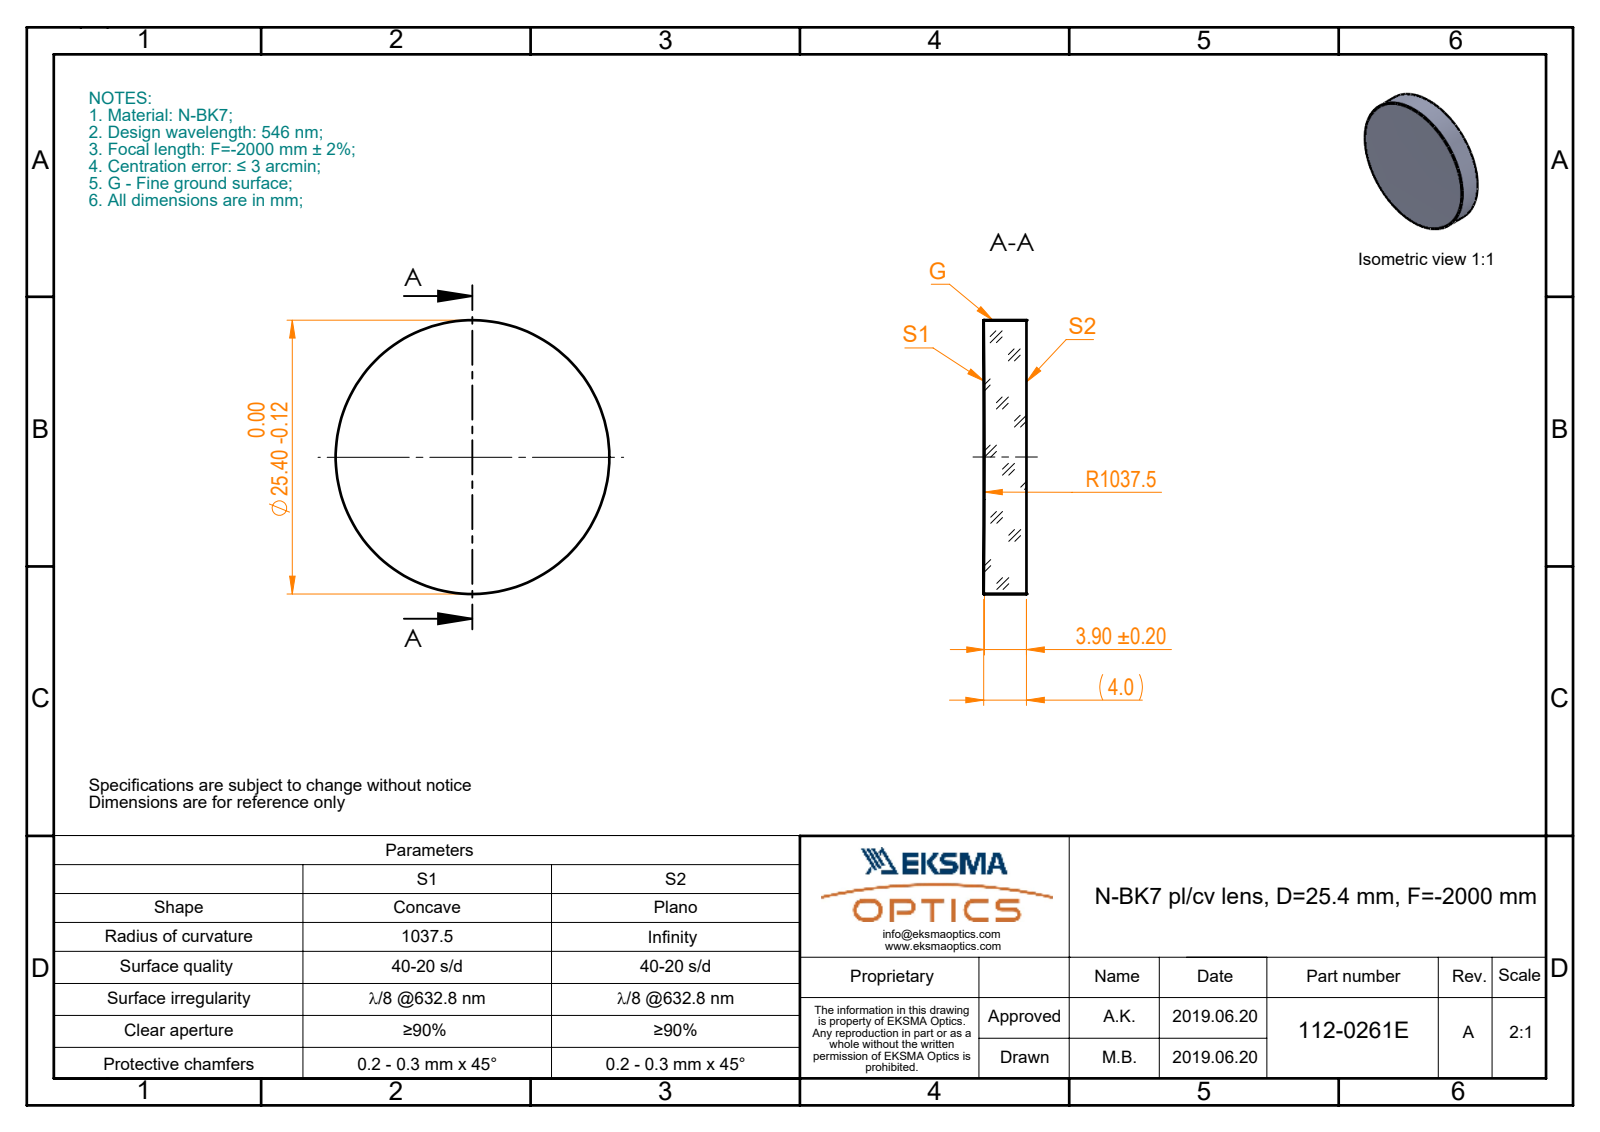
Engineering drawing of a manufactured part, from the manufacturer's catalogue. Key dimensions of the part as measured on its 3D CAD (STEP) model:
Part name (STEP PRODUCT): 112-0261E BK7 pl-cv 25.4 F-2000
STEP written by: SolidWorks 2017 (CONFIG_CONTROL_DESIGN)
Units: millimetres
Bodies: 1 solid, 5 faces (1 planar, 2 cylindrical, 2 other)
Overall size (bounding box): 25.4 × 25.4 × 3.98
Volume: 1 996 mm³ · Surface area: 1 331 mm²
Round bosses / shafts (diameter × count): ⌀25.4 ×1
